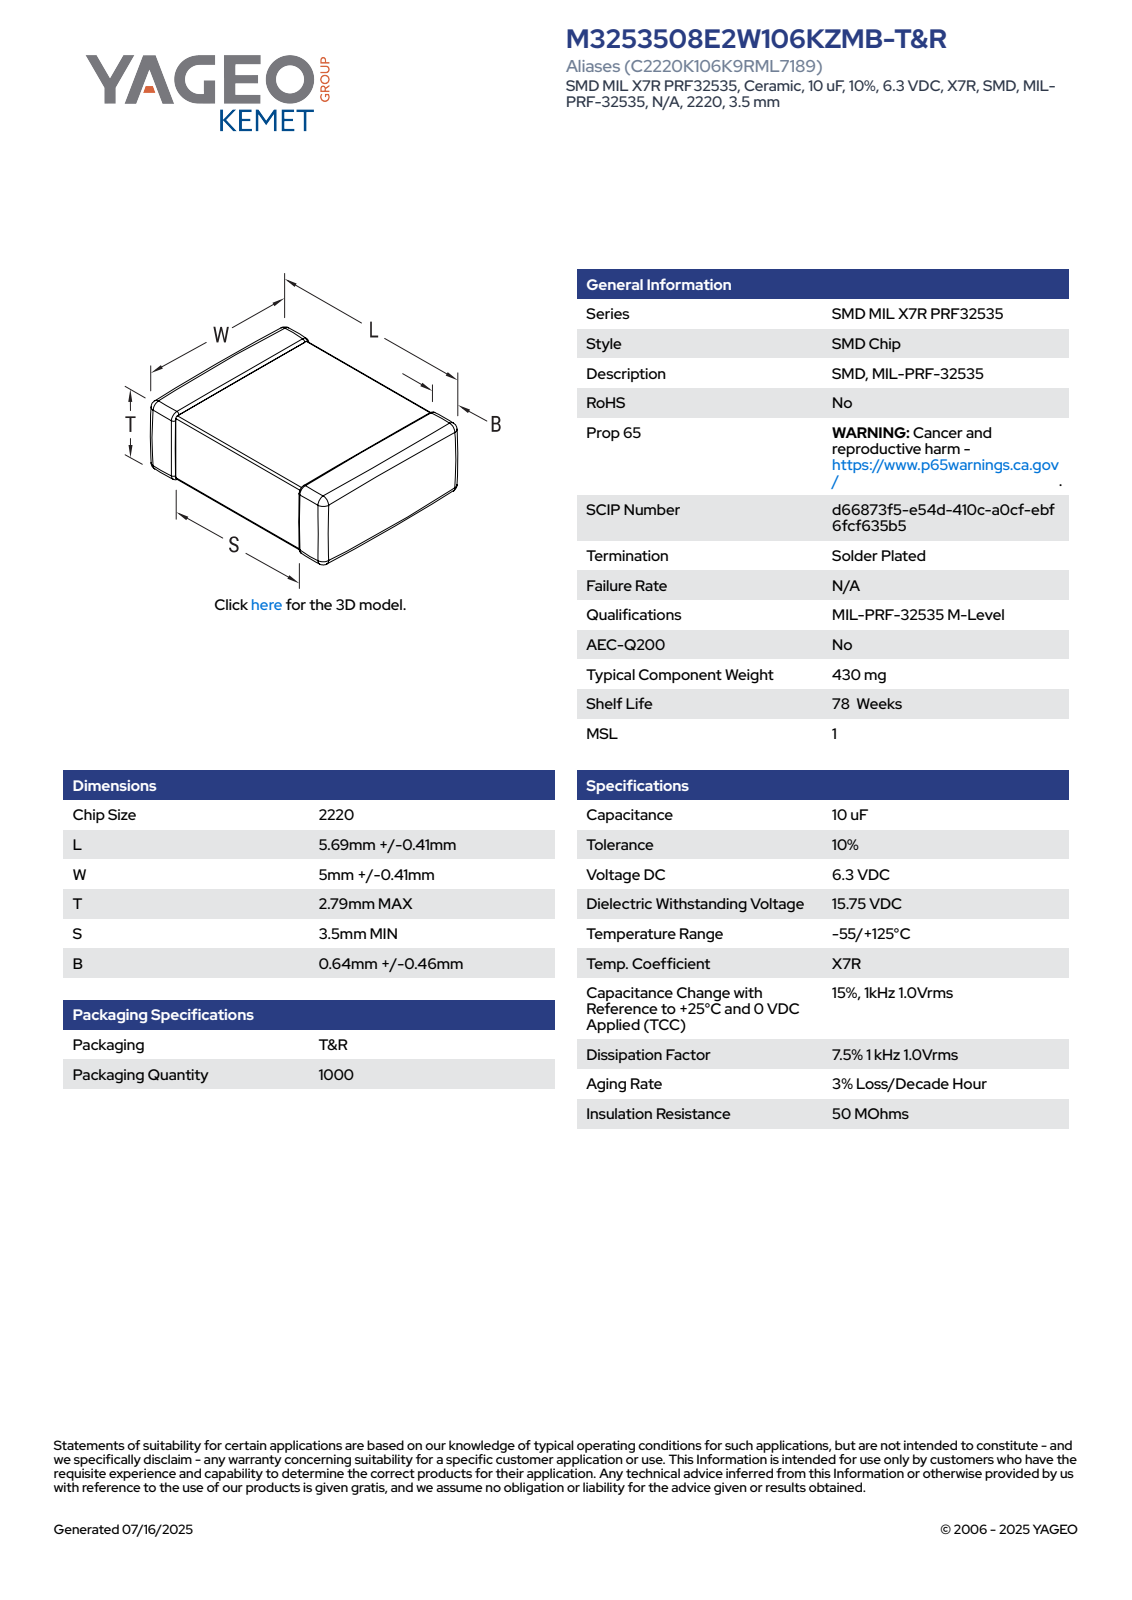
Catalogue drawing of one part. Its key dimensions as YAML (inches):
part_name: "CCSM_STD_2220_L6.1W5.41T2.79S2.79B1.1"
step_written_by: "SolidWorks 2021 (AUTOMOTIVE_DESIGN)"
units: inches
bodies: {solids: 4, faces: 121, planar: 71, cylindrical: 34, other: 16}
overall_size: [0.24, 0.213, 0.11]
volume: 0.005
surface_area: 0.202
partial_cylinders:
  - {radius: 0.004, count: 24}
face_to_face_distances: [0.101, 0.106, 0.24, 0.204, 0.11, 0.209, 0.213, 0.098, 0.142, 0.13]
